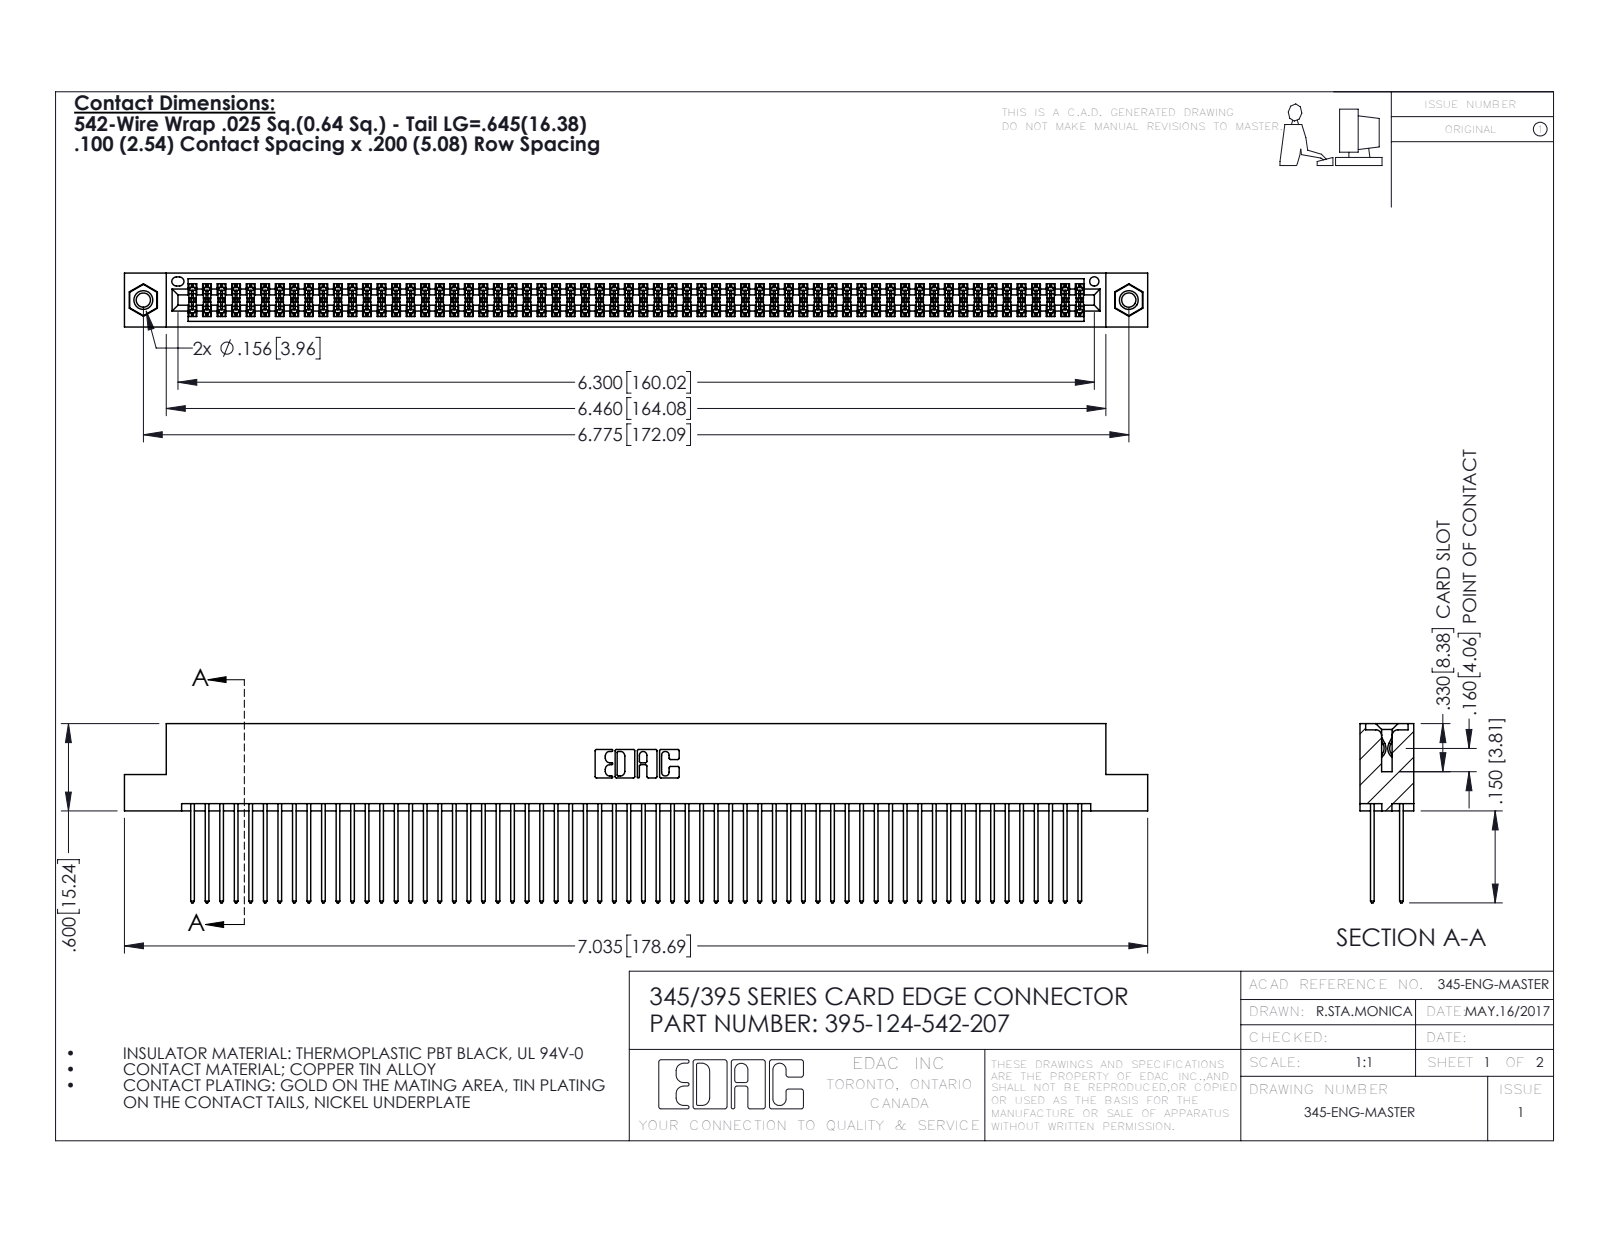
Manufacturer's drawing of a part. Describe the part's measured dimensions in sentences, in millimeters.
The part is named "395-124-542-207; 345-292-001_345-293-142; 345-250-001_345-250-005-103; 345 Part_Flush Mounting Lugs - 0.156 Dia-TI". Its 3-D file was written by "SolidWorks 2016 (CONFIG_CONTROL_DESIGN)". It is 127 solids with 6386 faces: 4204 planar, 2166 cylindrical and 16 other. Overall it measures 178.7 by 31.3 by 9.4 millimeters. Its volume is 18 110 cubic millimeters and its surface area 29 880 square millimeters. Round holes: 2 of diameter 2.5, 2 of diameter 3.2, 2 of diameter 4, 1 of diameter 1.6. Round bosses or shafts: 2 of diameter 3.9. Partial cylindrical surfaces (rounded edges, fillets, slot ends): 186 of radius 0.2, 124 of radius 0.3, 22 of radius 0.3, 6 of radius 0.2, 6 of radius 0.8, 3 of radius 0.7, 2 of radius 0.4, 2 of radius 0.5. The main face-to-face distances are 1.8, 7.6, 5.1, 2.5, 6.9, 0.6, 5.7, 9.4, 4.4, 3.8. The hole center spacings are 6.9, 166.1, 172.1.
